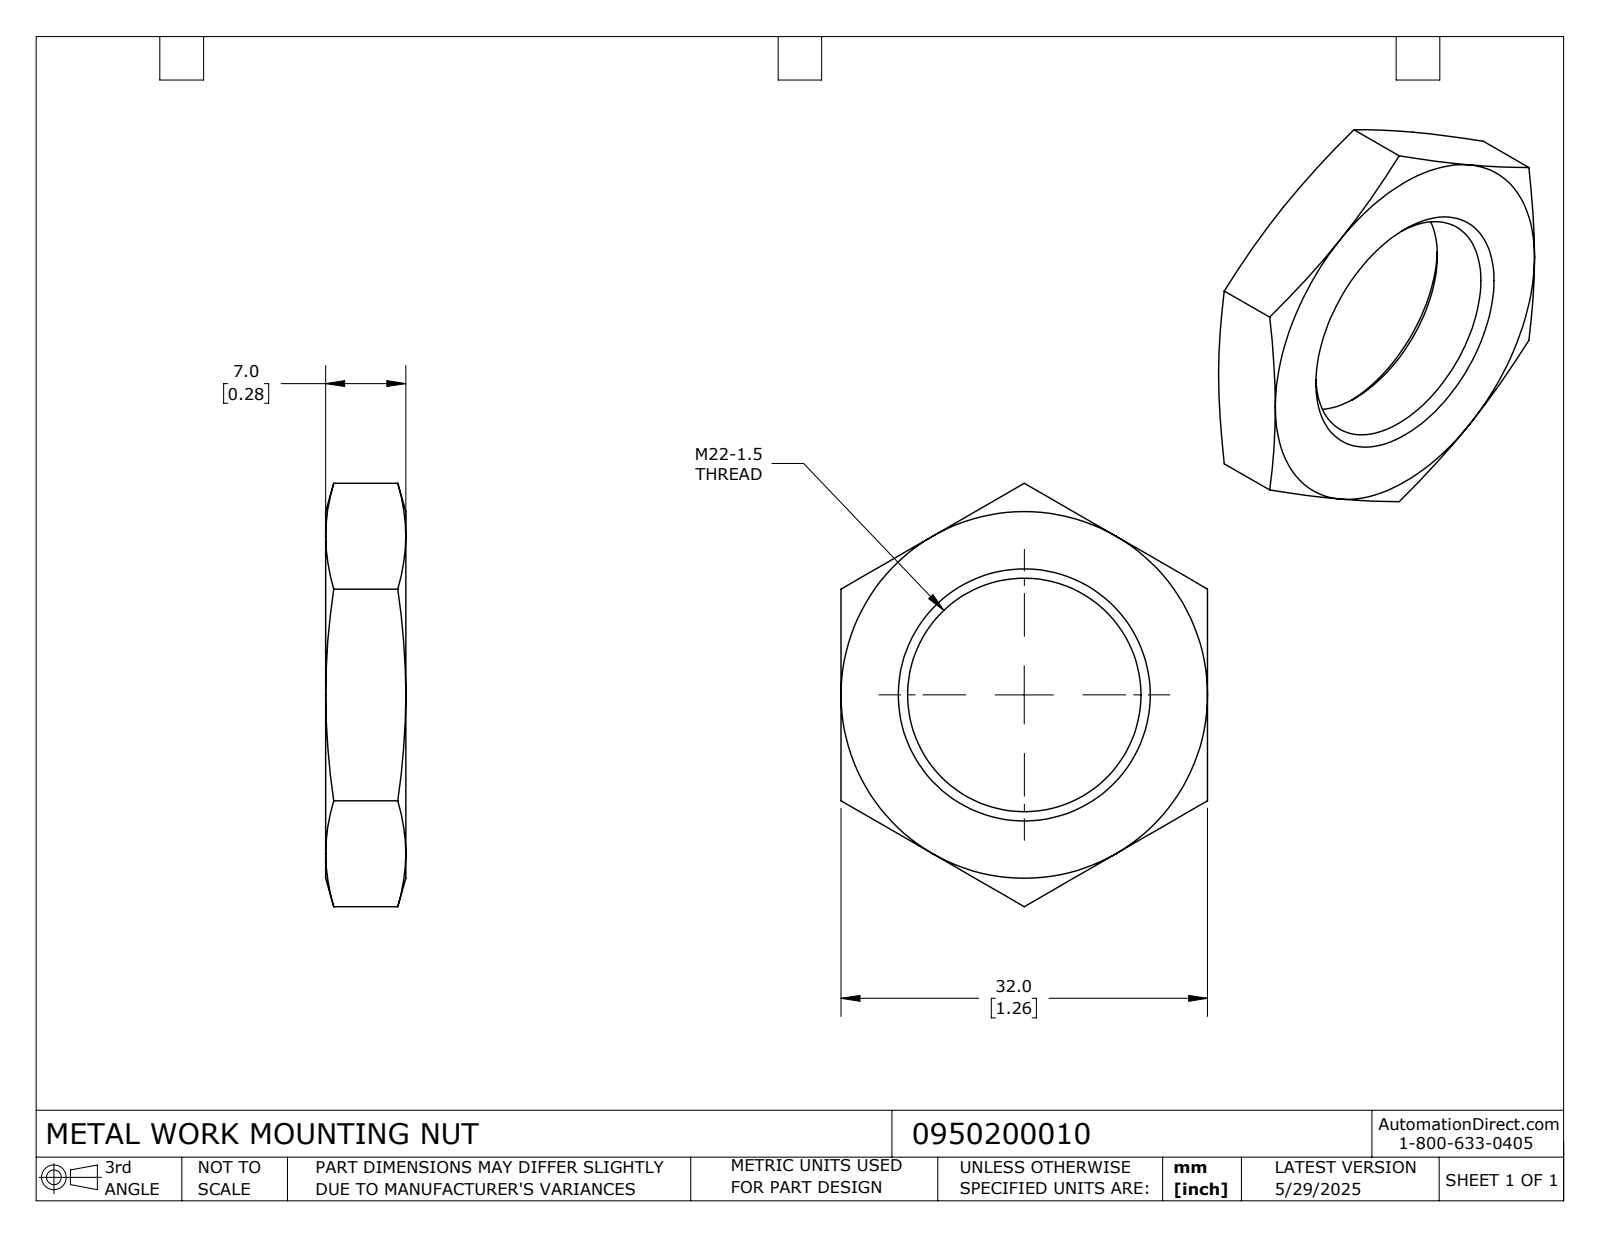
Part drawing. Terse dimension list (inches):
name: 0950200010
written by: SolidWorks 2024 (CONFIG_CONTROL_DESIGN)
unit: in
bodies: 1 solid, 26 faces (8 planar, 2 cylindrical, 16 other)
size: 1.455 × 1.26 × 0.276
volume: 0.235 in³; area: 3.472 in²
holes: 1× ⌀0.802
face distances: 0.276, 1.26
